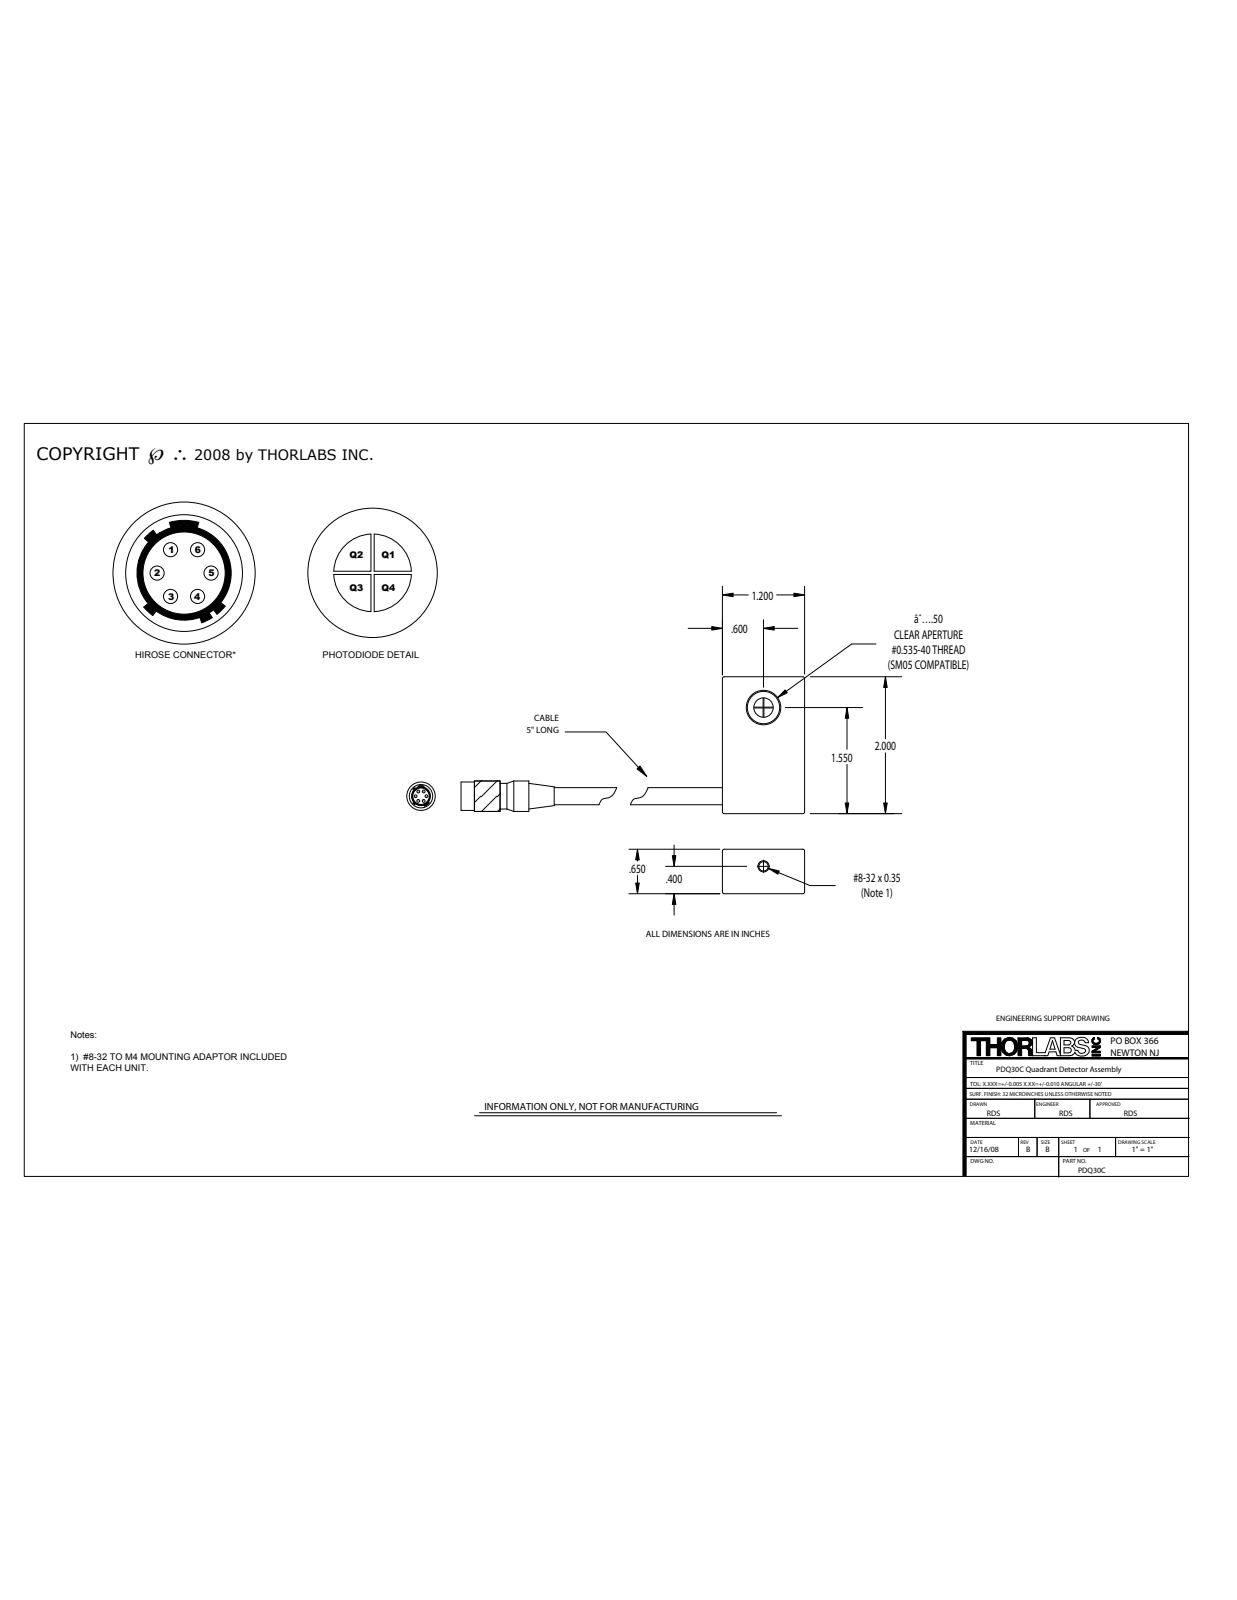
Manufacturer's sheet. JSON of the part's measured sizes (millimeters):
{"part_name": "test1", "step_written_by": "SolidWorks 2007 (AUTOMOTIVE_DESIGN)", "units": "millimeters", "bodies": {"solids": 0, "faces": 453, "planar": 255, "cylindrical": 47, "other": 151}, "overall_size": [50.8, 35.37, 16.55], "round_holes": [[2.18, 2], [0.32, 1], [0.96, 1], [1.78, 1], [4.17, 1], [5.59, 1], [13.97, 1], [14.48, 1]], "round_bosses_or_shafts": [[3.63, 2], [0.5, 1]], "partial_cylinders_radius": [[0.64, 12], [1.02, 8], [0.15, 1]], "face_to_face_distances": [16.5, 30.48, 50.8, 1.27, 29.21, 16.52, 8.9, 7.6, 1.39, 1.4], "hole_center_spacings": [2.41, 8.05, 34.9, 37.19]}
